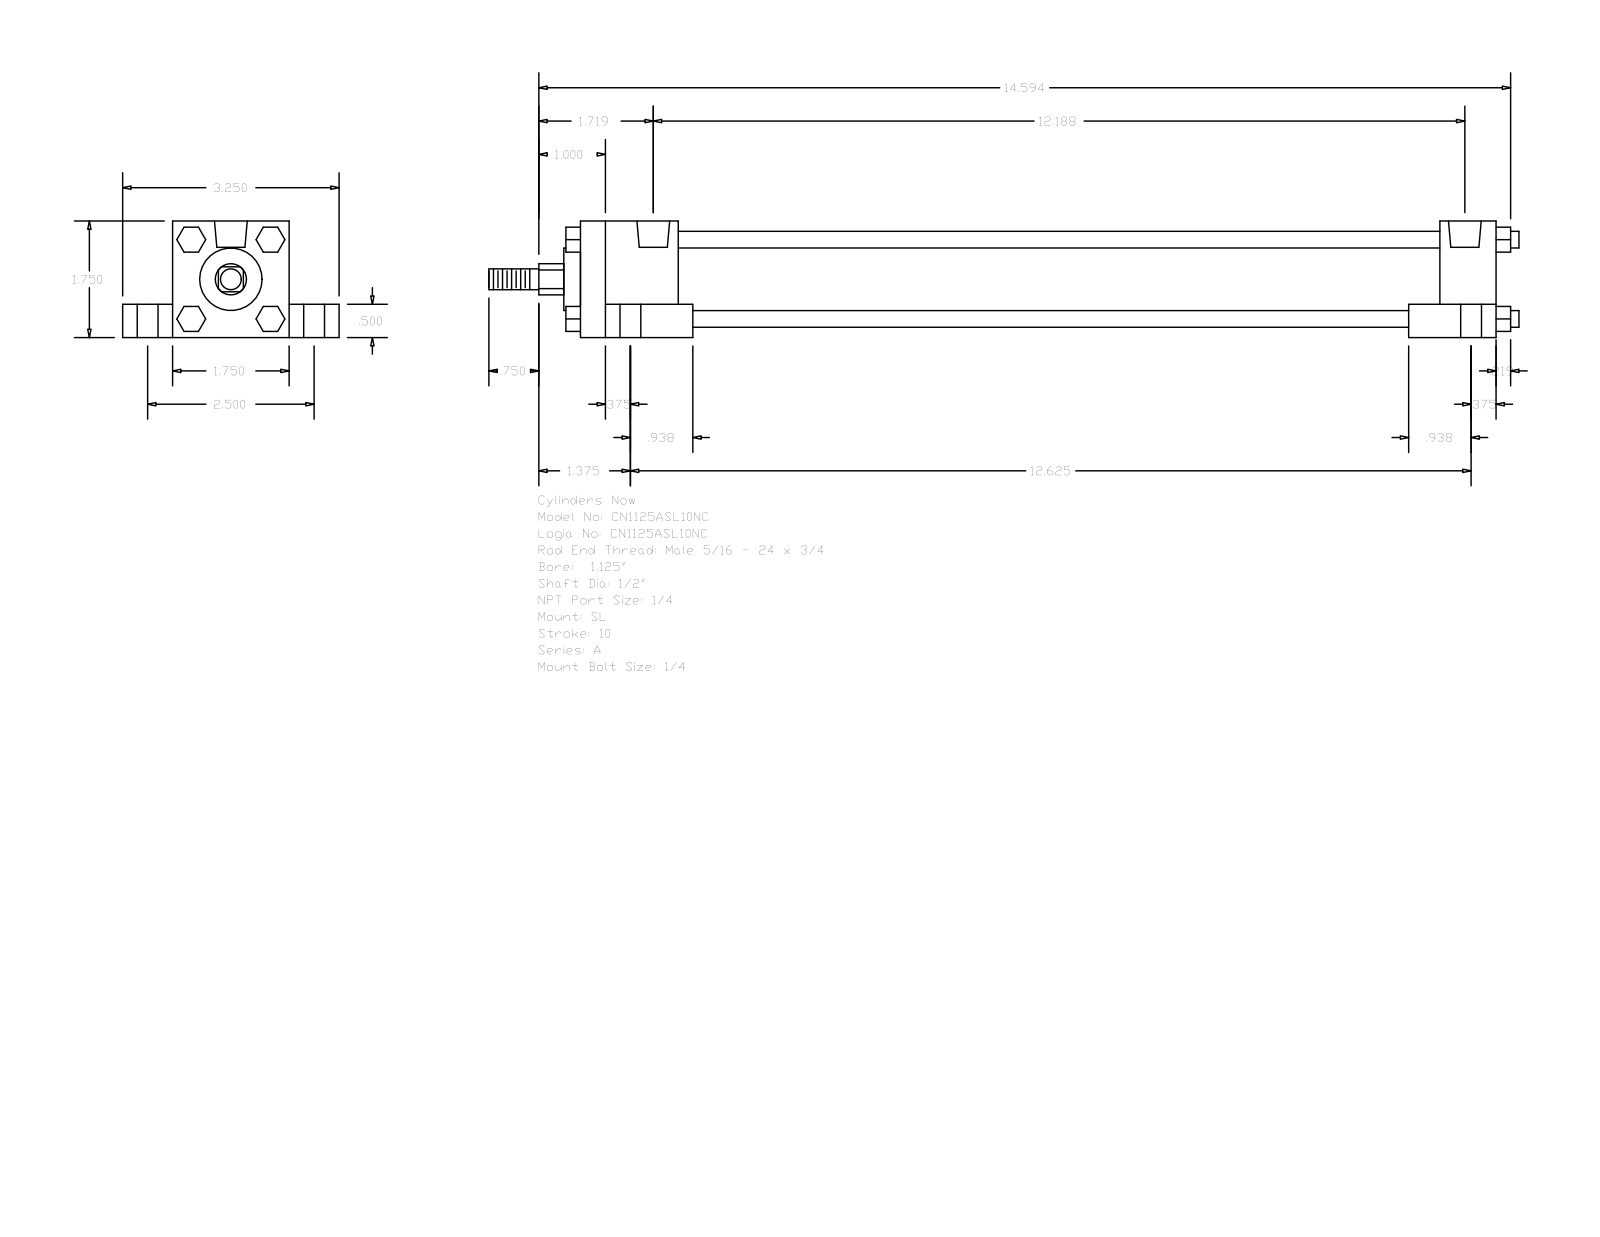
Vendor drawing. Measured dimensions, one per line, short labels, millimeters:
name: A_SL__0112_0.5
written by: GSSL Pune (CONFIG_CONTROL_DESIGN)
unit: mm
bodies: 0 solids, 150 faces (114 planar, 36 cylindrical, 0 other)
size: 392.91 × 82.55 × 44.45
holes: 4× ⌀5.56, 4× ⌀7.94, 4× ⌀14.29, 2× ⌀12.49
bosses: 4× ⌀6.35, 1× ⌀31.88, 1× ⌀23.81, 1× ⌀12.7, 1× ⌀7.94
rounds: 1× R5.94
face distances: 44.46, 31.76, 12.7, 19.04, 63.5, 311.94, 349.24, 327.81, 21.43, 37.3
hole spacings: 31.84, 32, 32.93, 33.39, 63.5, 306.39, 311.98, 313.55
